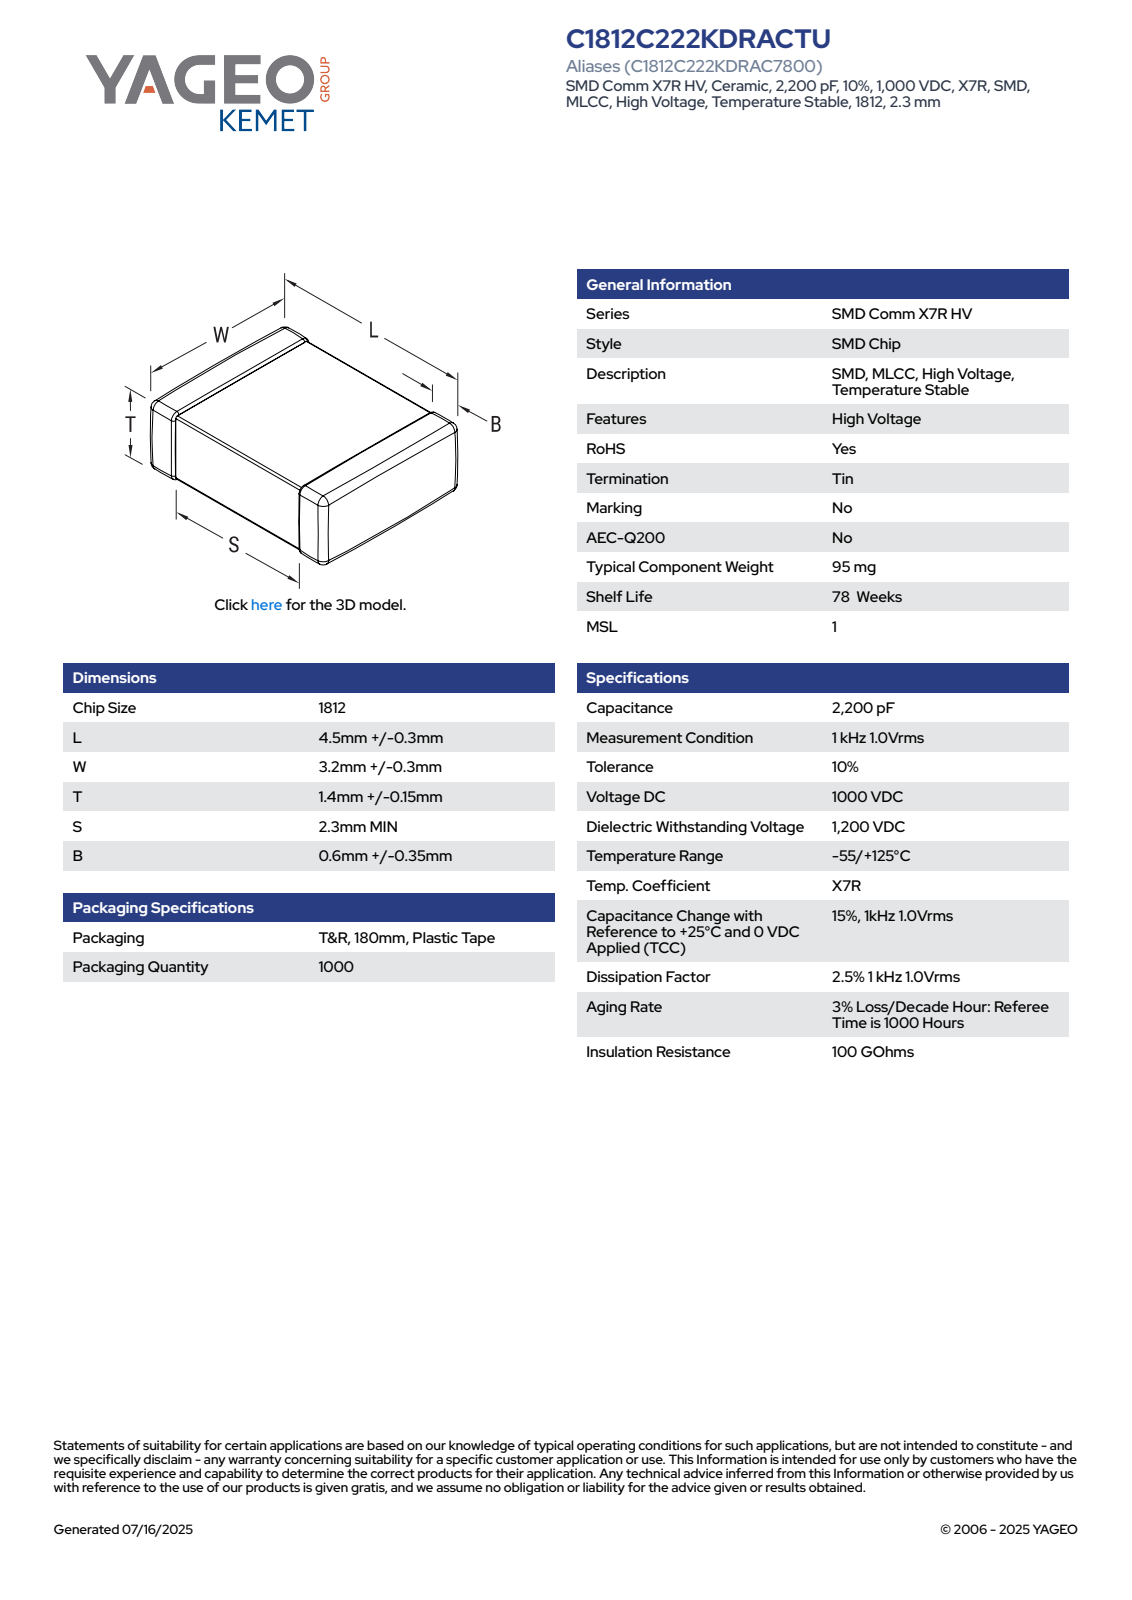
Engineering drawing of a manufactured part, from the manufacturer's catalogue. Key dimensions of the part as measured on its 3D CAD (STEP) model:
Part name (STEP PRODUCT): CCS_CCSTDNOS_1812_L4.8W3.5T1.55B0.95
STEP written by: SolidWorks 2014 (AUTOMOTIVE_DESIGN)
Units: millimetres
Bodies: 4 solids, 125 faces (71 planar, 38 cylindrical, 16 other)
Overall size (bounding box): 4.8 × 3.5 × 1.55
Volume: 24 mm³ · Surface area: 58 mm²
Main face-to-face distances: 1.48, 1.41, 1.55, 4.8, 3.43, 3.36, 3.5, 1.49, 0.34, 1.94
